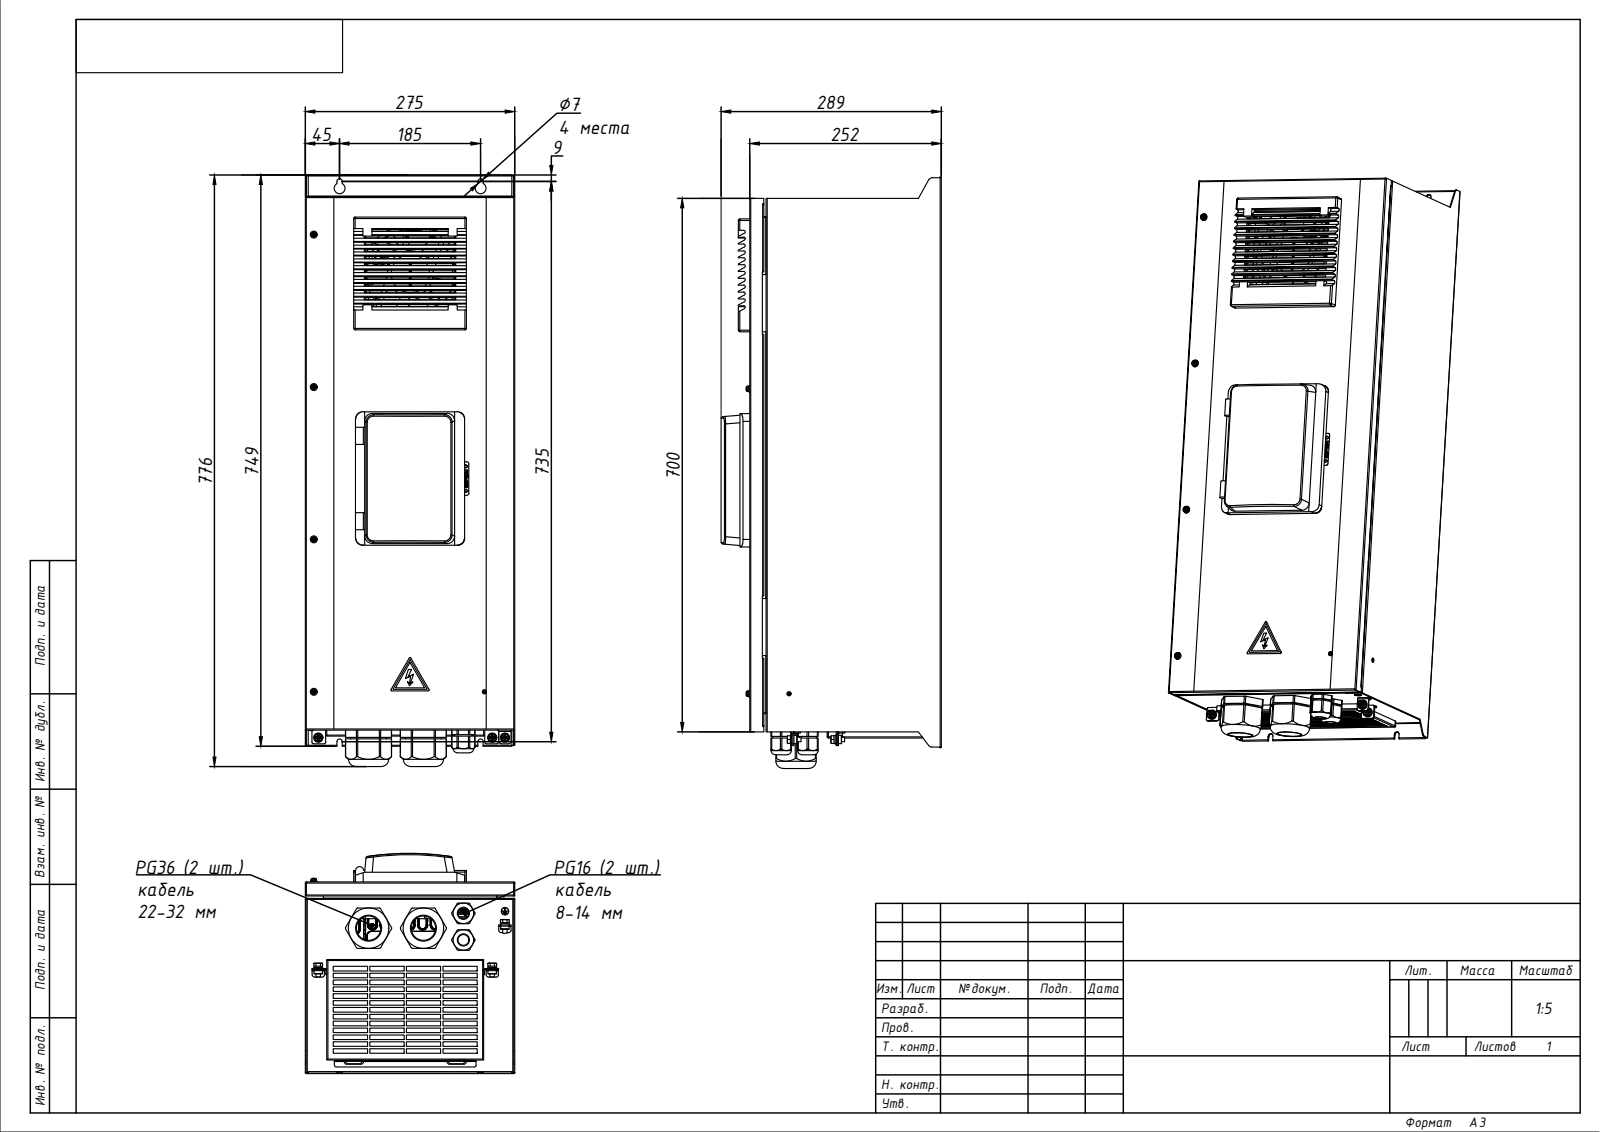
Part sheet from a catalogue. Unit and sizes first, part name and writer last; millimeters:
Units: millimetres
Overall size (bounding box): 785.5 × 290 × 275
Round holes (diameter × count): ⌀14 ×4, ⌀14.6 ×2, ⌀15.5 ×2, ⌀17.5 ×2, ⌀20.6 ×2, ⌀22 ×2, ⌀32.5 ×2, ⌀33 ×2, ⌀34.5 ×2, ⌀40 ×2, ⌀45.6 ×2, ⌀47 ×2
Round bosses / shafts (diameter × count): ⌀53 ×2, ⌀51.5 ×2, ⌀44 ×2, ⌀40.5 ×2, ⌀27 ×2, ⌀25 ×2, ⌀20 ×2, ⌀17.8 ×2
Partial cylindrical surfaces — rounded edges, fillets, slot ends (radius × count): R2 ×30, R5 ×12, R1 ×4, R3.5 ×4, R10 ×4, R3 ×2, R14.25 ×2, R15.15 ×2
Main face-to-face distances: 252, 275, 700, 1, 7, 707, 8, 708, 38, 2.5
Hole centre spacings: 35, 54.74, 56, 72, 125.46, 126.02, 185
Volume: 49 750 000 mm³ · Surface area: 1 231 000 mm²
Bodies: 24 solids, 1693 faces (1179 planar, 188 cylindrical, 326 other)
Part name (STEP PRODUCT): VF-101-P37K-0075-A-T4-C54-B-H - VF-101-P45K-0090-A-T4-C54-B-H; Корпус 4; Крышка; Решетка 5 148мм (+3 more)
STEP written by: C3D Toolkit (AP242_MANAGED_MODEL_BASED_3D_ENGINEERING_MIM_LF)
